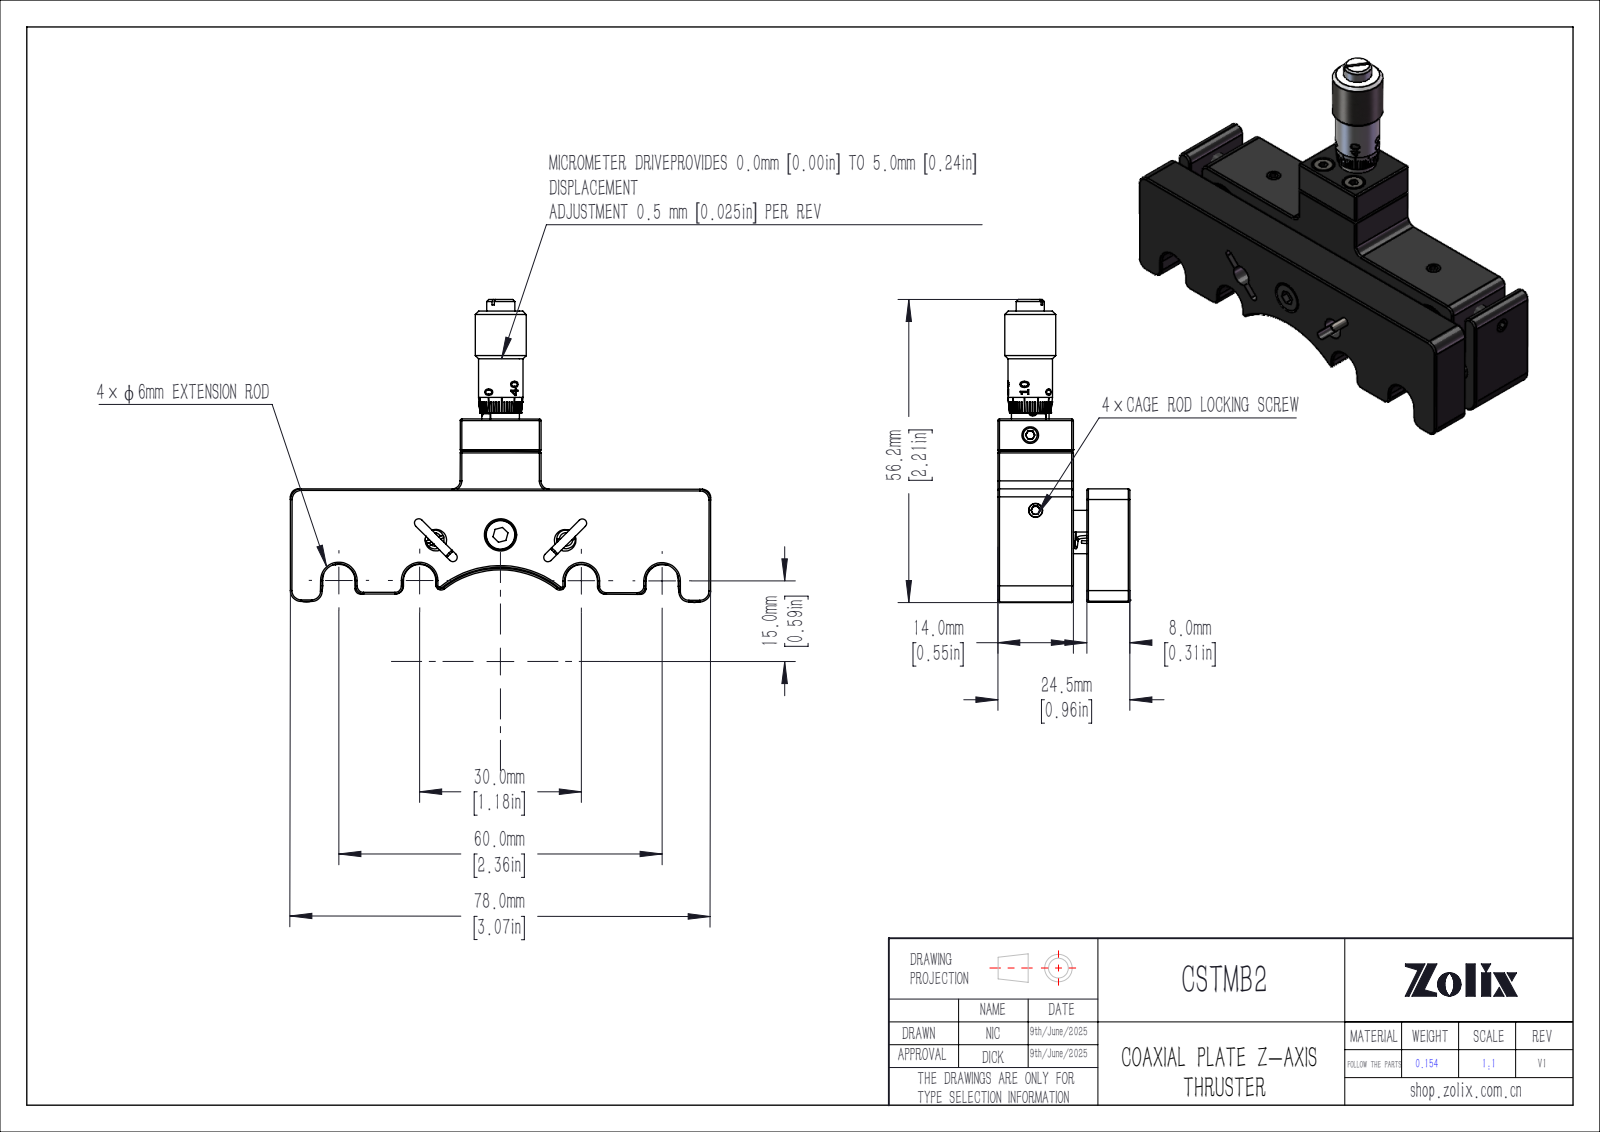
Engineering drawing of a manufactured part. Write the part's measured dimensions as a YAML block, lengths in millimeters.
part_name: "CSTMB1"
step_written_by: "SolidWorks 2020 (CONFIG_CONTROL_DESIGN)"
units: millimeters
bodies: {solids: 26, faces: 1206, planar: 456, cylindrical: 351, other: 399}
overall_size: [79.62, 60.68, 24.5]
volume: 30106
surface_area: 20230
round_holes:
  - {diameter: 2.5, count: 6}
  - {diameter: 4, count: 4}
  - {diameter: 8, count: 4}
  - {diameter: 1.6, count: 2}
  - {diameter: 2.4, count: 2}
  - {diameter: 4.3, count: 2}
  - {diameter: 5, count: 2}
  - {diameter: 6, count: 2}
  - {diameter: 3.4, count: 1}
  - {diameter: 3.51, count: 1}
  - {diameter: 7, count: 1}
  - {diameter: 7.24, count: 1}
round_bosses_or_shafts:
  - {diameter: 3, count: 6}
  - {diameter: 1.6, count: 4}
  - {diameter: 2, count: 3}
  - {diameter: 3.8, count: 2}
  - {diameter: 9.45, count: 1}
  - {diameter: 8.26, count: 1}
  - {diameter: 8, count: 1}
  - {diameter: 6.99, count: 1}
partial_cylinders:
  - {radius: 0.3, count: 104}
  - {radius: 1.5, count: 20}
  - {radius: 1, count: 10}
  - {radius: 3, count: 6}
  - {radius: 0.8, count: 4}
  - {radius: 1.3, count: 4}
  - {radius: 2, count: 4}
  - {radius: 3.1, count: 4}
face_to_face_distances: [16.5, 2.5, 24.5, 8, 10.5, 14, 7, 7.01, 78.03, 6.99]
hole_center_spacings: [6.4, 21.02, 21.03, 6.41, 12.04, 15.89, 17.47, 25.32]
